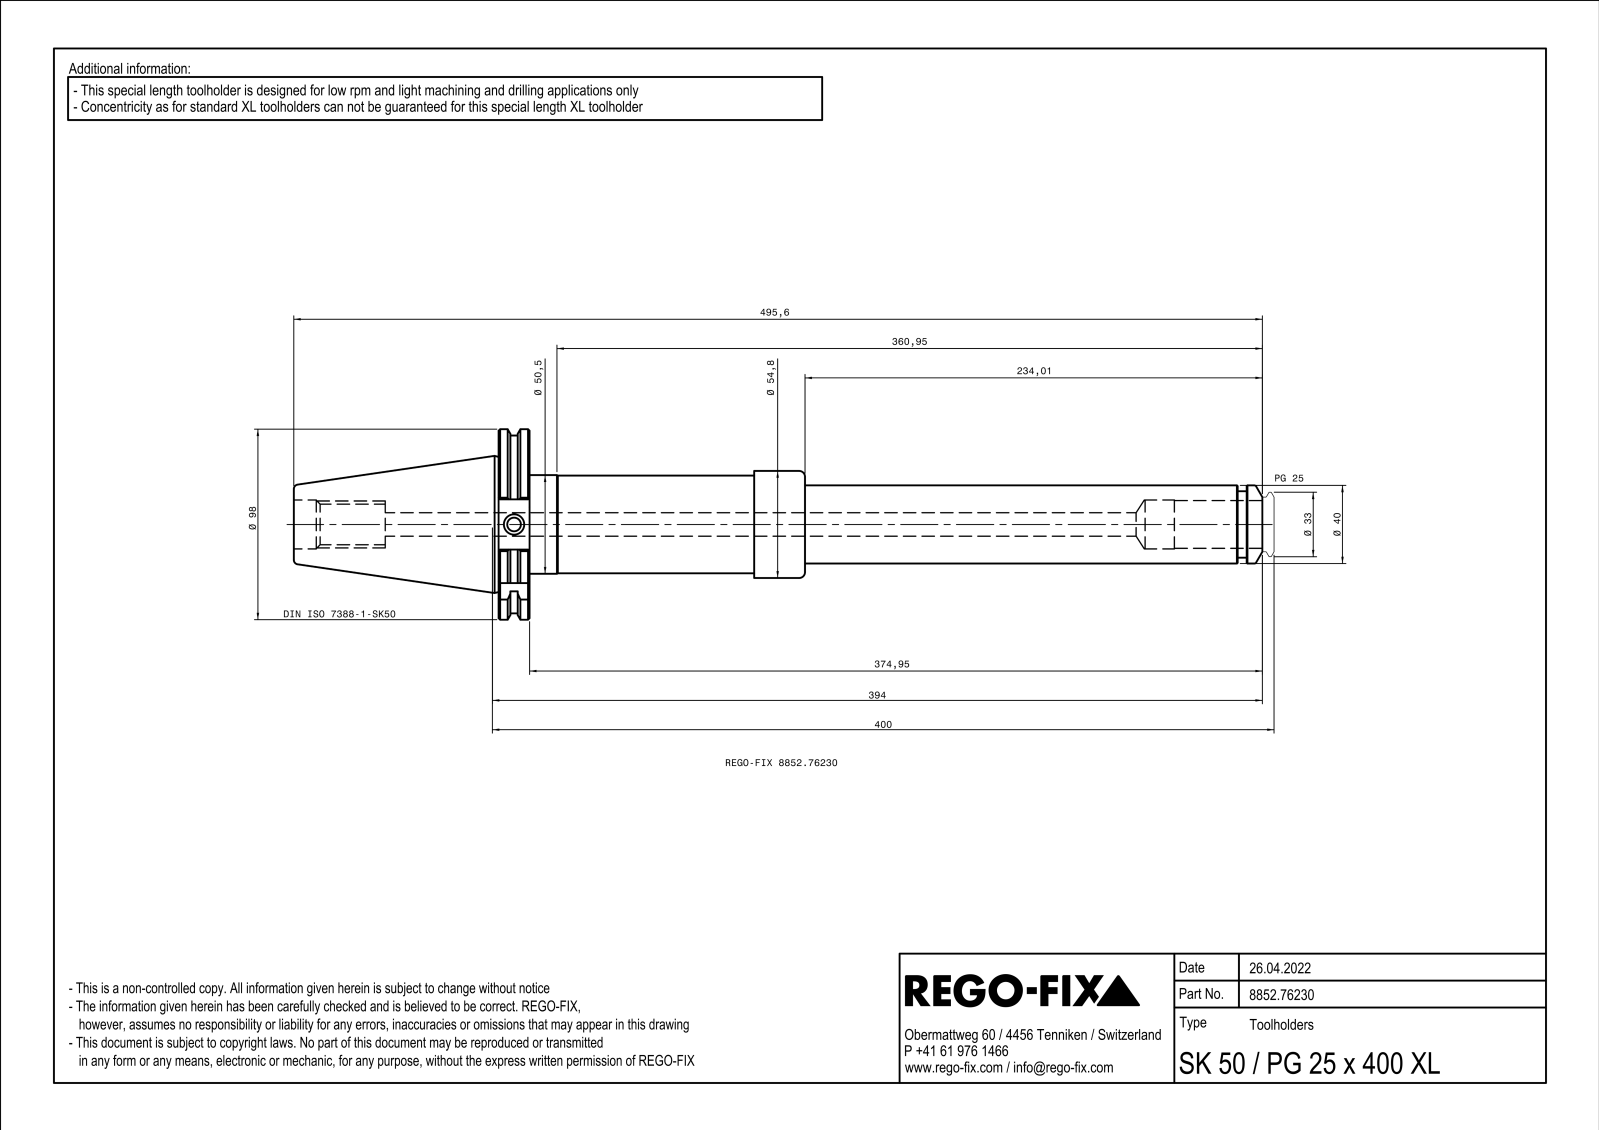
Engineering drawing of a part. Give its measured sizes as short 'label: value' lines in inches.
name: NOCUT
written by: SIEMENS PLM Software Solid Edge ST10 (AUTOMOTIVE_DESIGN)
unit: in
bodies: 1 solid, 168 faces (57 planar, 40 cylindrical, 71 other)
size: 19.512 × 3.839 × 3.684
volume: 49.03 in³; area: 195.8 in²
holes: 1× ⌀0.276, 1× ⌀0.394, 1× ⌀0.472, 1× ⌀0.512, 1× ⌀0.551, 1× ⌀0.817, 1× ⌀0.984, 1× ⌀1.299, 1× ⌀1.583, 1× ⌀1.905, 1× ⌀1.97, 1× ⌀2.02
bosses: 1× ⌀3.583, 1× ⌀2.157, 1× ⌀1.988, 1× ⌀1.969, 1× ⌀1.772, 1× ⌀1.654, 1× ⌀1.575, 1× ⌀1.339
rounds: 5× R0.02, 1× R1.077, 1× R1.919
face distances: 0.624, 5.549, 6.173, 0.315, 5.234, 5.858, 2.637, 2.323, 2.911, 3.535
